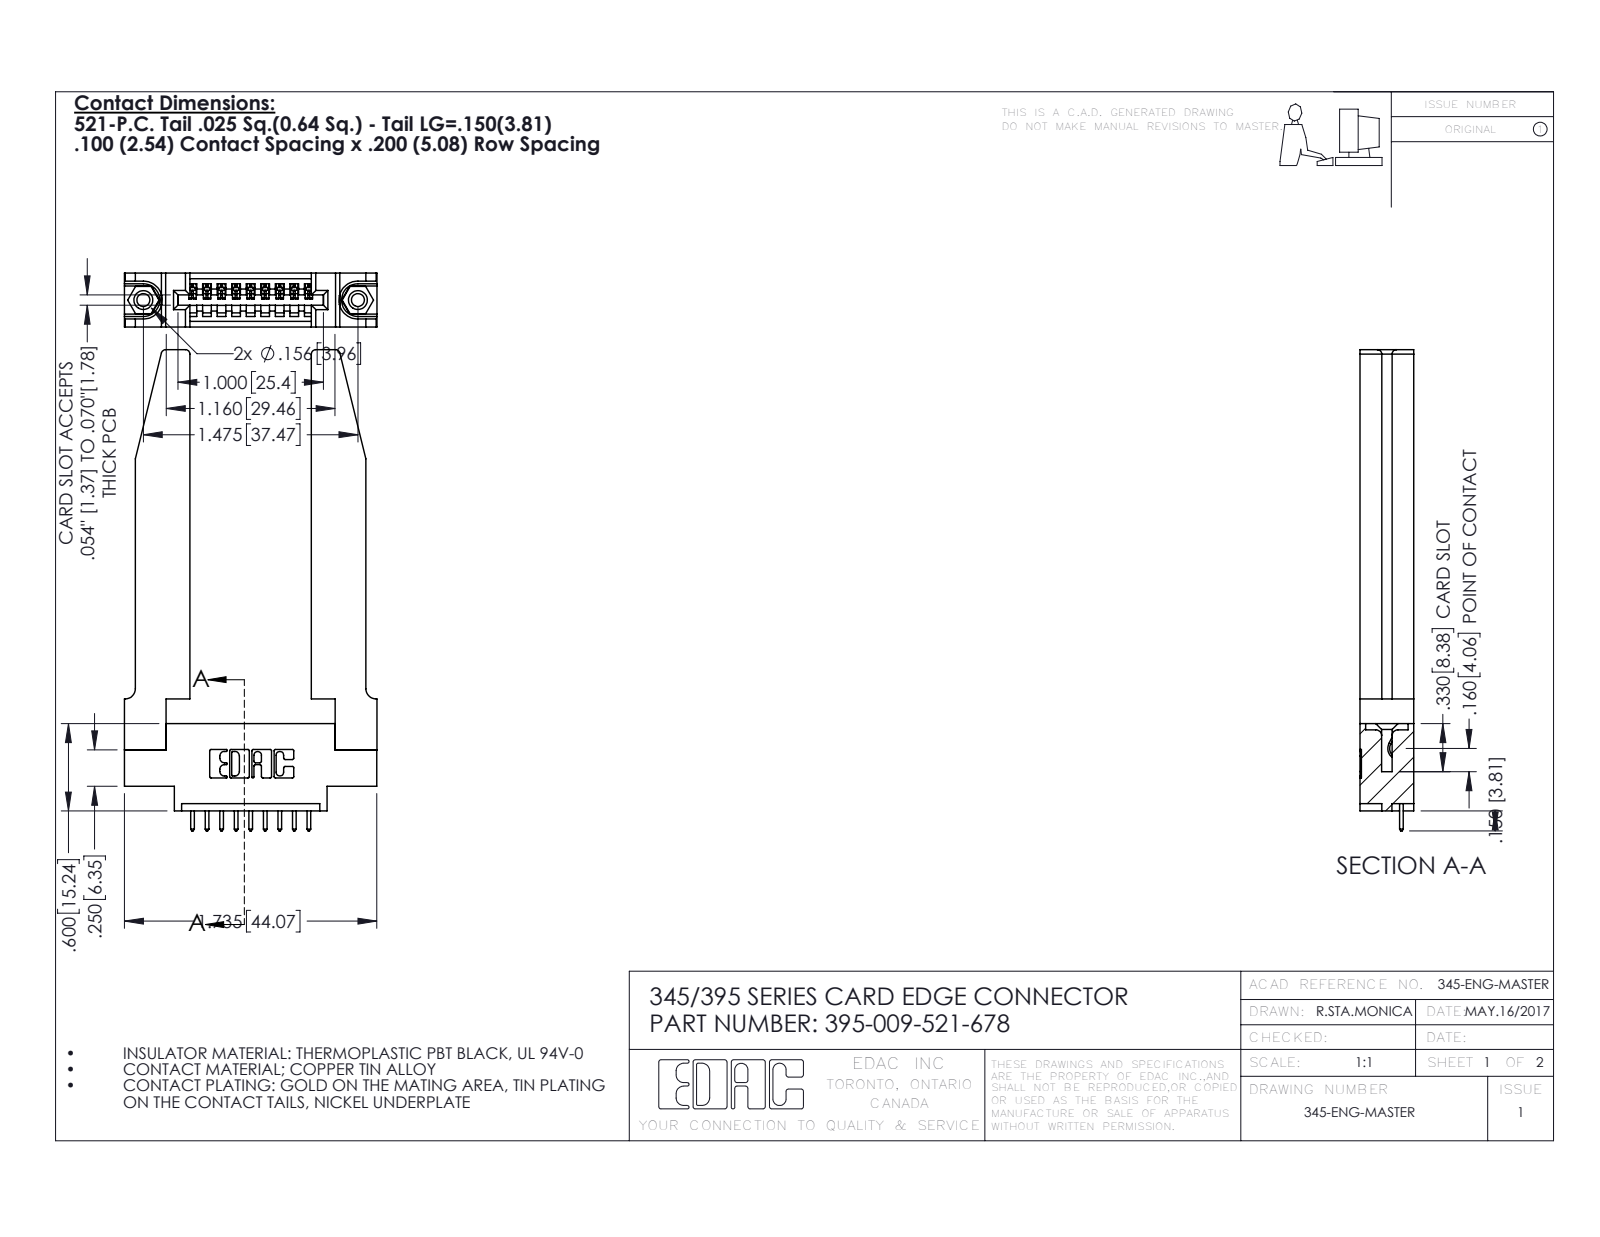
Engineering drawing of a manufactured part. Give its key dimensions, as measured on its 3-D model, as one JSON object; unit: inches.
{"part_name": "345-250-001_345-250-001-102; 345-220-078_345-220-078; 395-009-521-678; 345 Part_0.170 Offset - 0.156 Dia-TH (+1 more)", "step_written_by": "SolidWorks 2016 (CONFIG_CONTROL_DESIGN)", "units": "inches", "bodies": {"solids": 14, "faces": 886, "planar": 586, "cylindrical": 248, "other": 52}, "overall_size": [3.307, 1.736, 0.37], "volume_in3": 0.705, "surface_area_in2": 17.74, "round_holes": [[0.089, 2], [0.125, 2], [0.156, 2], [0.064, 1]], "round_bosses_or_shafts": [[0.155, 2]], "partial_cylinders_radius": [[0.01, 22], [0.006, 18], [0.01, 18], [0.03, 8], [0.007, 6], [0.031, 6], [0.026, 3], [0.031, 2]], "face_to_face_distances": [0.37, 0.072, 0.15, 0.298, 0.148, 0.22, 0.077, 0.835, 0.095, 0.071], "hole_center_spacings": [0.27, 1.244, 1.475]}
